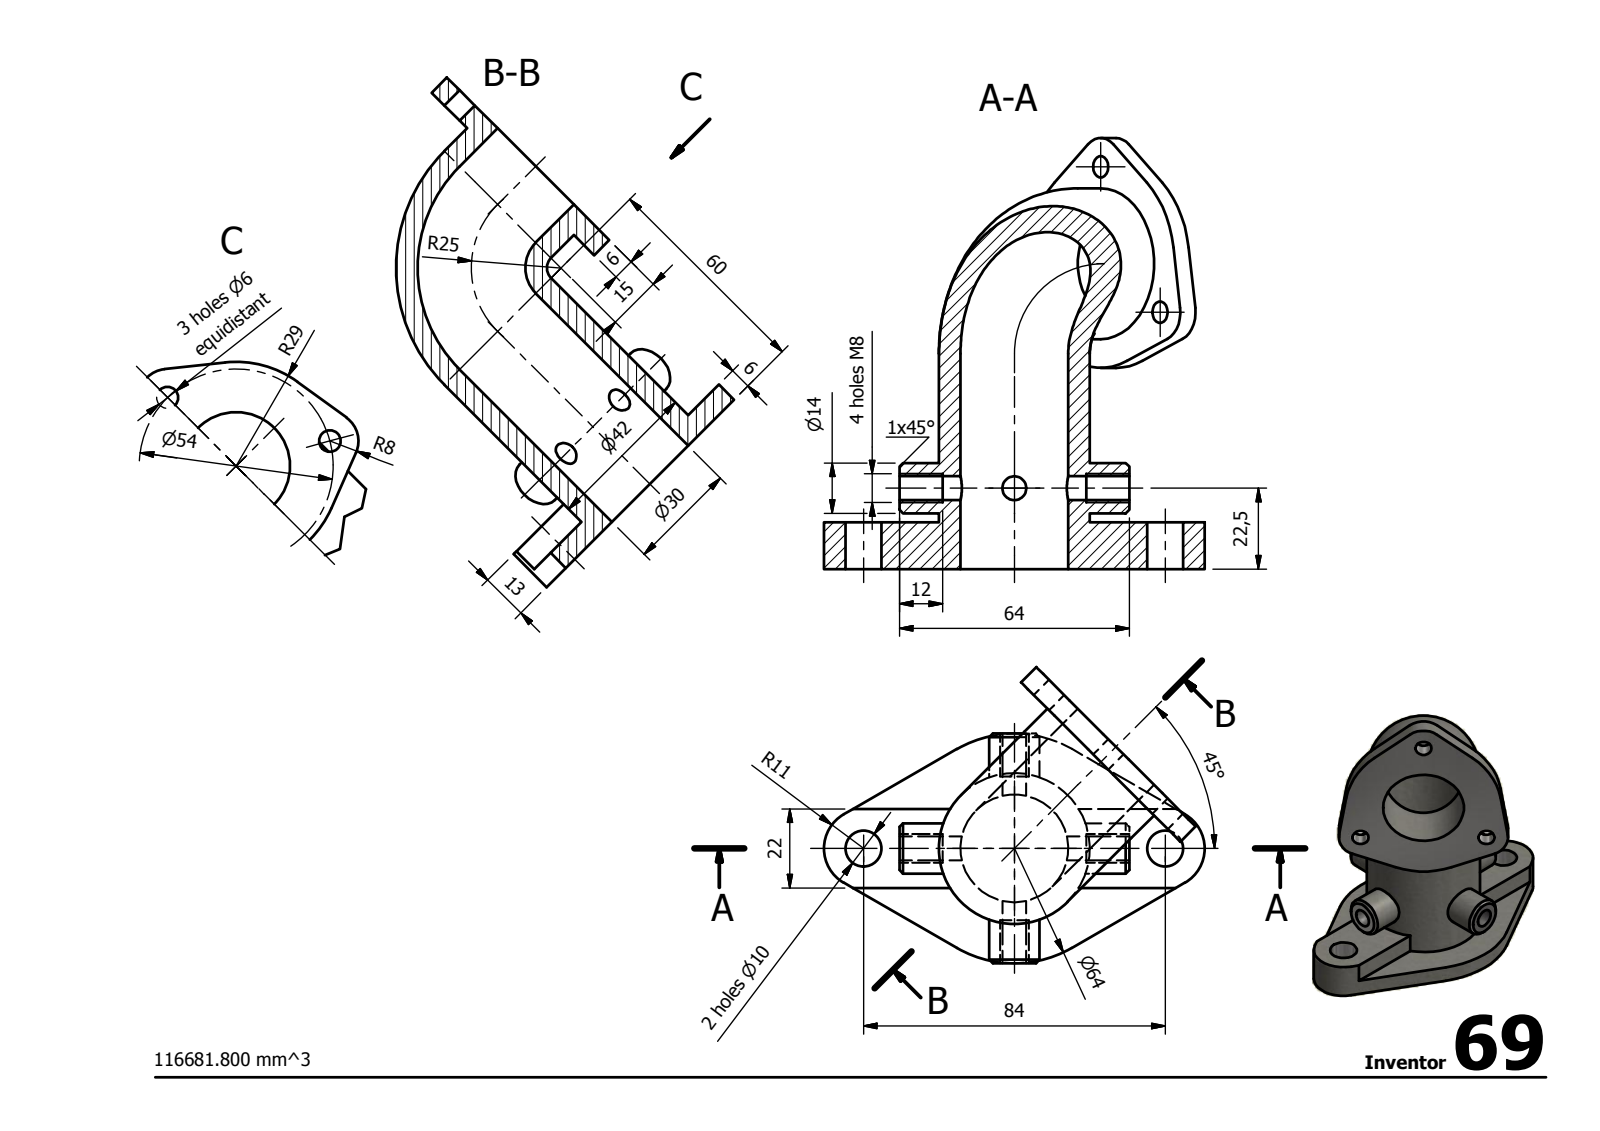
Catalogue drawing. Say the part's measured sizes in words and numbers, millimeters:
Its 3-D file was written by "Autodesk Inventor 2014 (AUTOMOTIVE_DESIGN)". It is 1 solid with 58 faces: 25 planar, 27 cylindrical and 6 other. Overall it measures 120 by 106 by 82.47 millimeters. Its volume is 116 697 cubic millimeters and its surface area 42 203 square millimeters. Round holes: 3 of diameter 6, 2 of diameter 6.65, 2 of diameter 10, 2 of diameter 30. Round bosses or shafts: 2 of diameter 42, 2 of diameter 14. Partial cylindrical surfaces (rounded edges, fillets, slot ends): 3 of radius 8, 2 of radius 11, 1 of radius 29, 1 of radius 32. The main face-to-face distances are 6, 13, 7, 64, 22, 21, 43. The hole center spacings are 27, 46.77, 42, 84.
